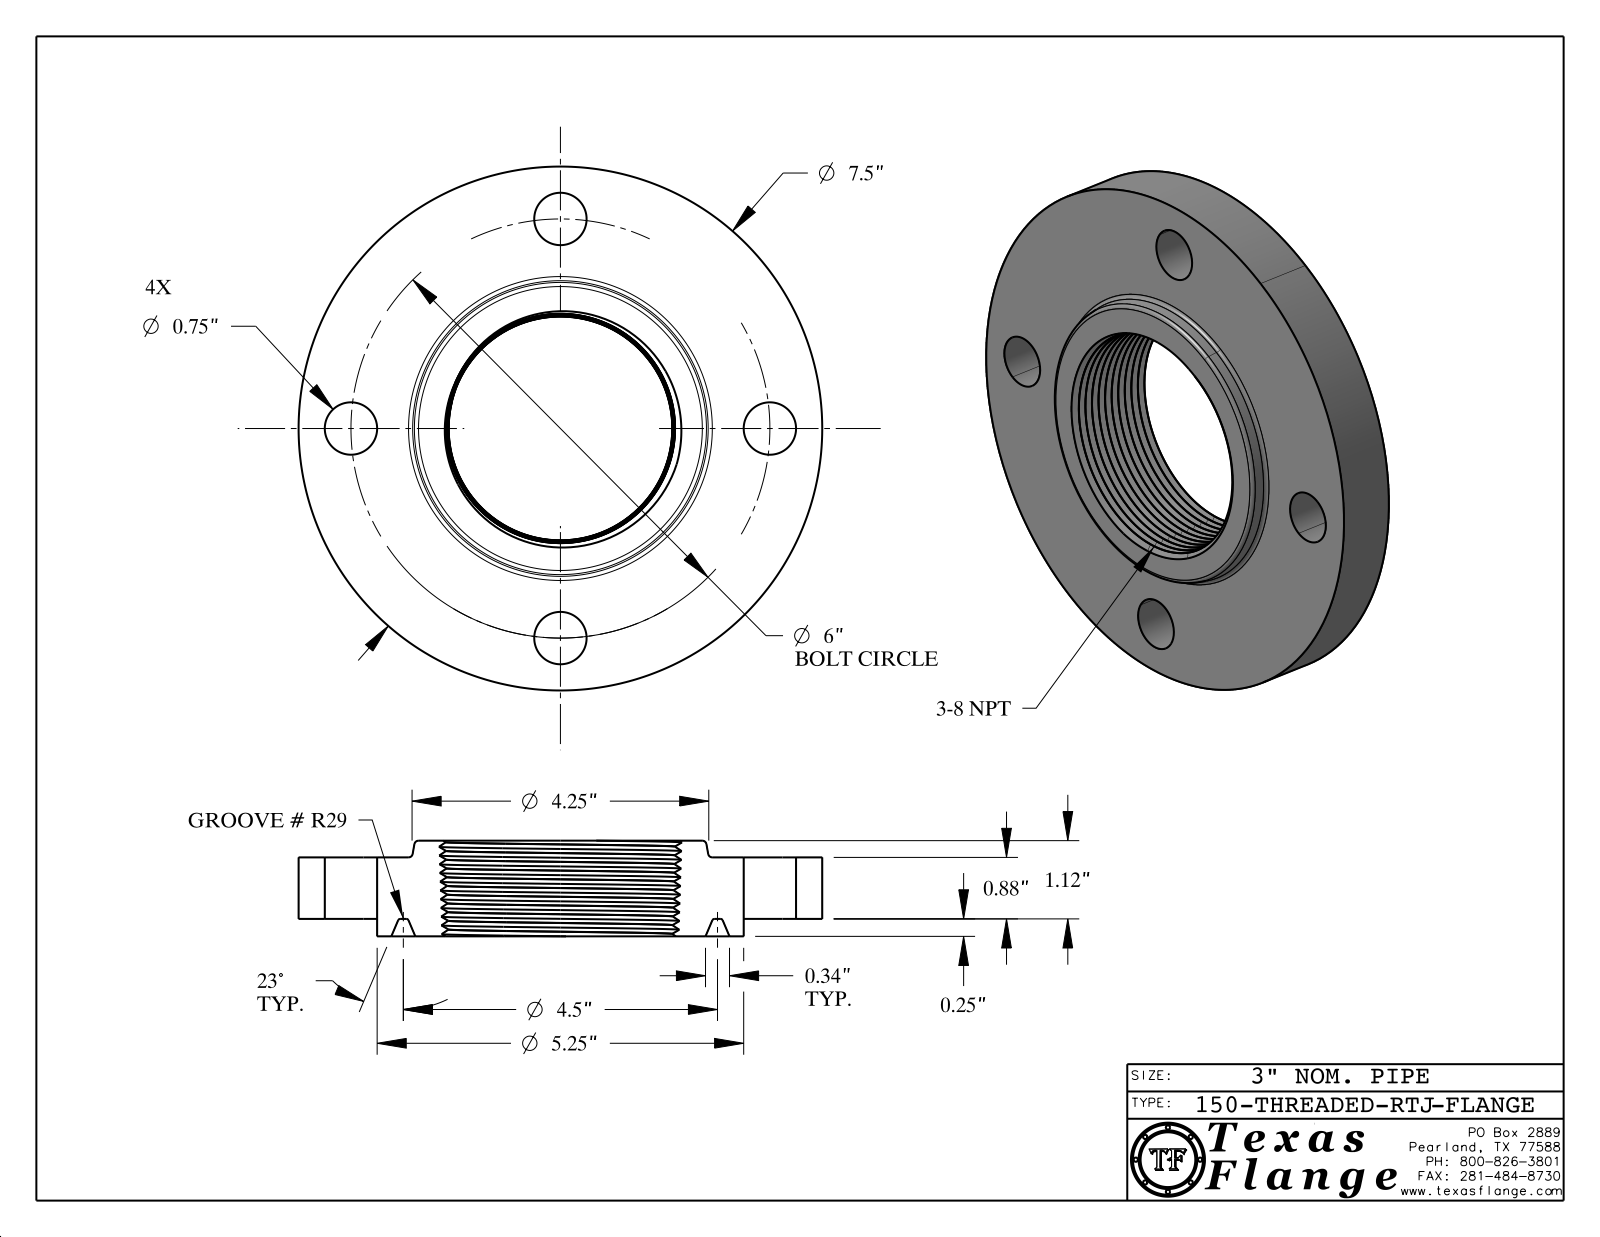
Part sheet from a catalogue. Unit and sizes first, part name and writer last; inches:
Units: inches
Overall size (bounding box): 7.5 × 7.5 × 1.37
Round holes (diameter × count): ⌀0.75 ×4, ⌀0.495 ×1
Round bosses / shafts (diameter × count): ⌀0.03 ×8, ⌀7.5 ×1, ⌀5.25 ×1, ⌀0.39 ×1
Main face-to-face distances: 0.88, 0.25, 1.13, 1.37, 1.12, 0.24, 1.115, 0.865, 0.015, 0.255
Hole centre spacings: 4.243, 2.296, 5.543, 6
Volume: 33.22 in³ · Surface area: 134.3 in²
Bodies: 1 solid, 534 faces (371 planar, 32 cylindrical, 131 other)
Part name (STEP PRODUCT): 150-THREADED-RTJ
STEP written by: CATIA V5 STEP AP214 (AUTOMOTIVE_DESIGN)
